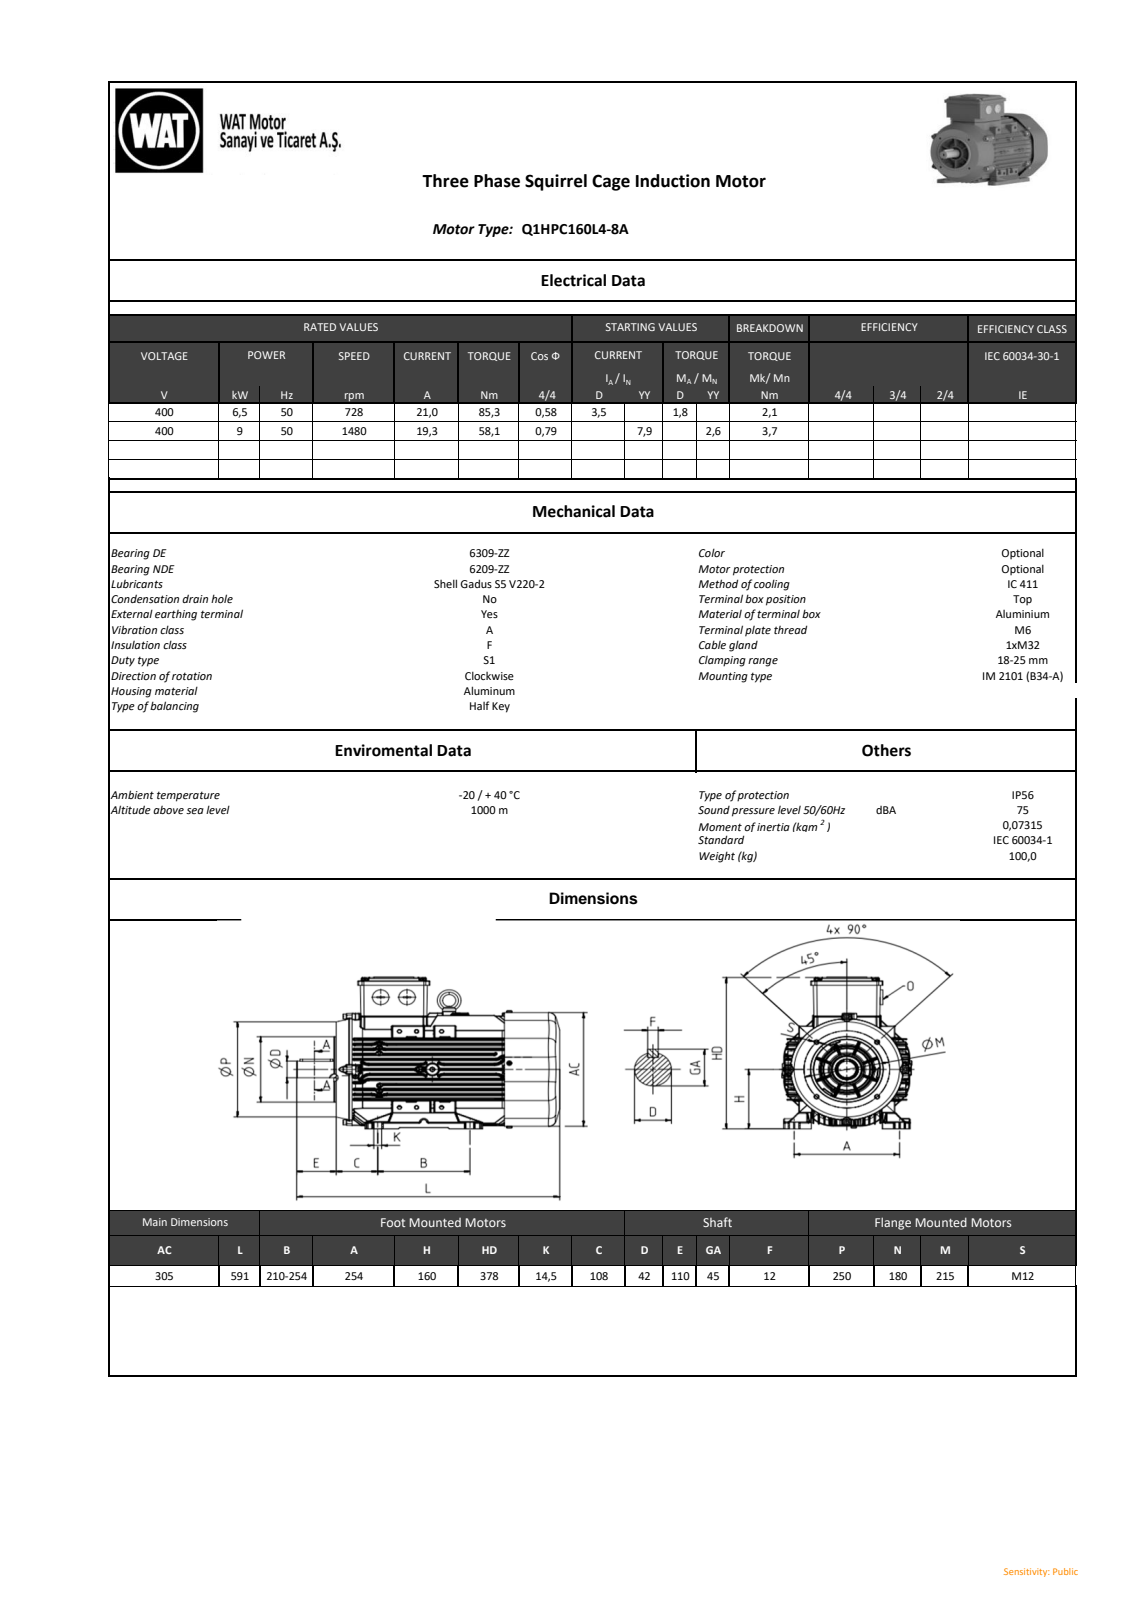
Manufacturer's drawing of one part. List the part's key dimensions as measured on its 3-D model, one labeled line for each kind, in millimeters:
Part name (STEP PRODUCT): DIS GORUNUS QH160 PC_x_t_objects
STEP written by: SIEMENS PLM Software NX2206.8101 (AP203_CONFIGURATION_CONTROLLED_3D_DESIGN_OF_MECHANICAL_PARTS_AND_ASSEMBLIES_MIM_LF)
Units: millimetres
Bodies: 0 solids, 7846 faces (2019 planar, 3058 cylindrical, 2769 other)
Overall size (bounding box): 591 × 377.75 × 314
Round holes (diameter × count): ⌀10.3 ×4, ⌀15 ×4, ⌀8 ×2, ⌀7 ×1, ⌀10 ×1, ⌀14 ×1, ⌀17 ×1, ⌀72 ×1, ⌀85.63 ×1, ⌀94 ×1, ⌀114 ×1, ⌀134 ×1
Round bosses / shafts (diameter × count): ⌀8 ×8, ⌀16 ×4, ⌀10 ×4, ⌀38 ×2, ⌀272.5 ×1, ⌀180 ×1, ⌀178 ×1, ⌀168 ×1
Partial cylindrical surfaces — rounded edges, fillets, slot ends (radius × count): R1 ×805, R0.5 ×567, R4 ×104, R5 ×62, R2 ×50, R2.5 ×48, R3 ×27, R5.5 ×16
Main face-to-face distances: 144, 168, 11.92, 9.62, 14.77, 168.39, 158.77, 24.39, 120, 11.85
Hole centre spacings: 100.99, 231.35, 142.5, 201.53, 107.49, 107.24, 107.47, 107.52
